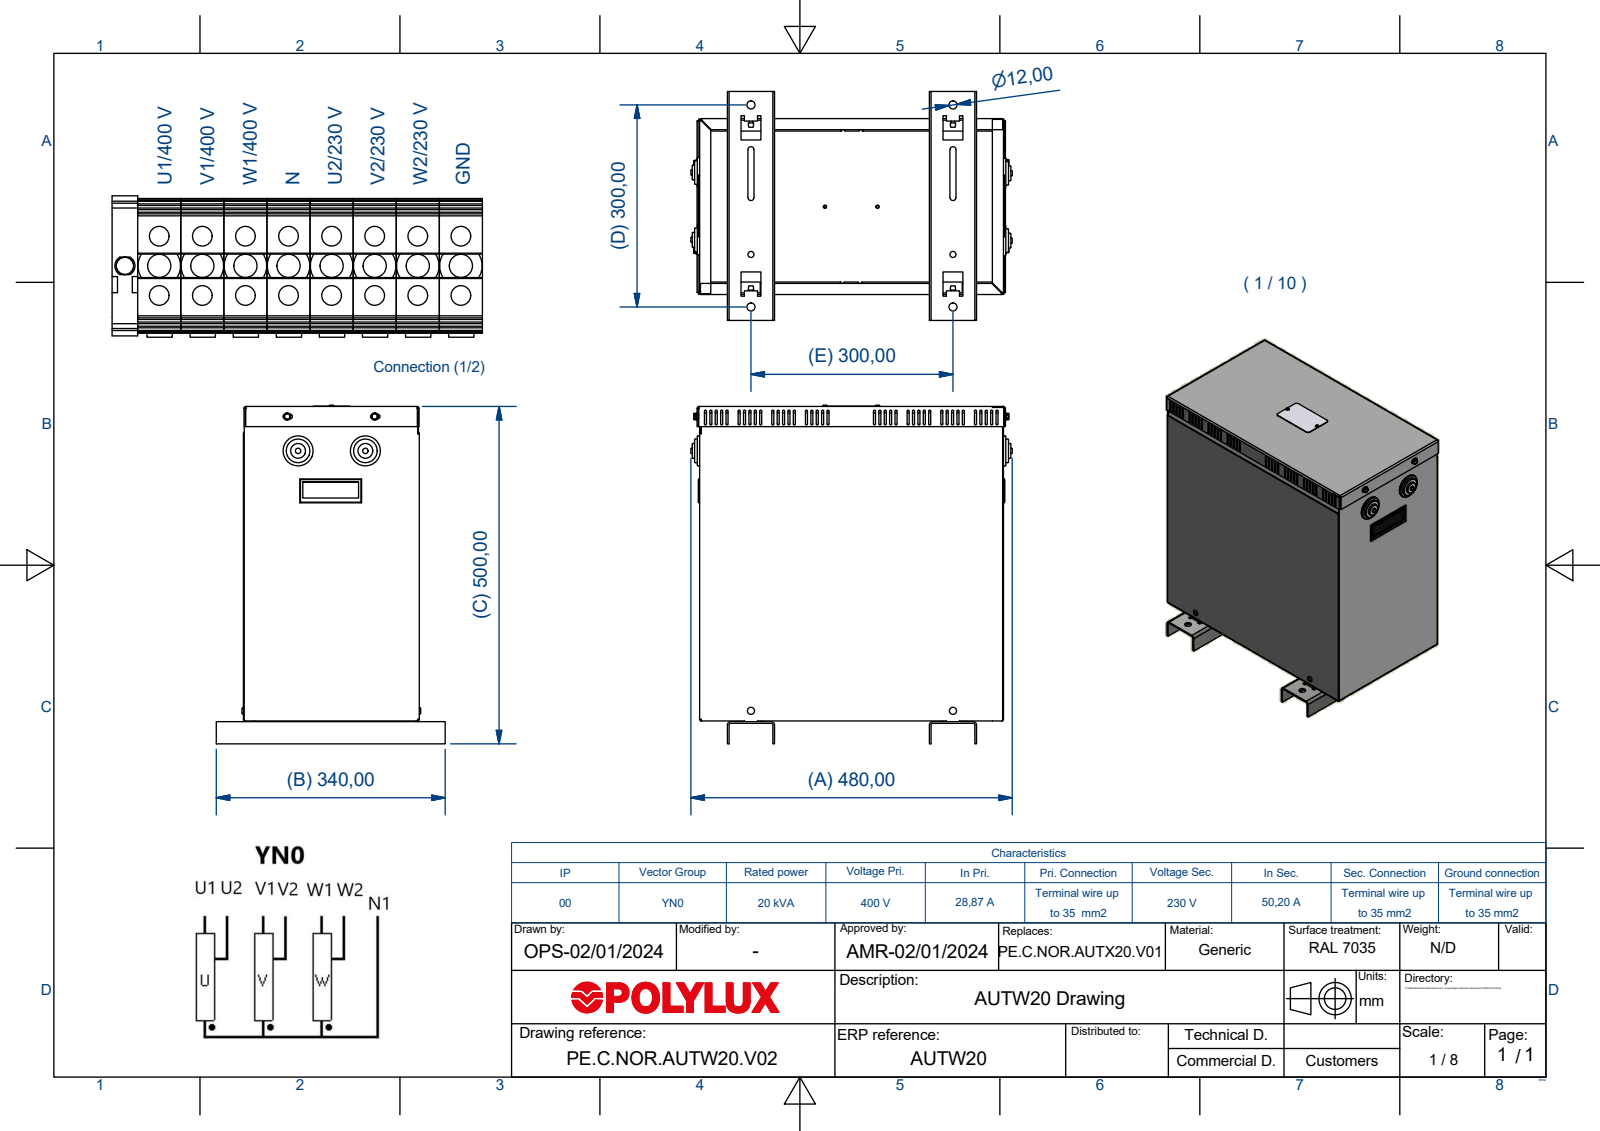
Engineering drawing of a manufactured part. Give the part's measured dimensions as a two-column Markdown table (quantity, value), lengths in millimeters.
| quantity | value |
| --- | --- |
| part name | AUTW20 |
| STEP written by | Autodesk Inventor 2018 (AUTOMOTIVE_DESIGN) |
| units | millimeters |
| bodies | 26 solids, 1132 faces (668 planar, 384 cylindrical, 80 other) |
| overall size | 502.8 × 477.2 × 340 |
| volume | 1 296 000 mm³ |
| surface area | 1 913 000 mm² |
| round holes (diameter × count) | 5.25 × 4, 5.6 × 4, 6 × 4, 8 × 4, 12 × 4, 20 × 4, 33 × 4, 36.5 × 4, 37 × 4, 42.5 × 4, 3.5 × 2, 4 × 2 |
| round bosses / shafts (diameter × count) | 5 × 6, 44.5 × 4, 38.5 × 4, 35 × 4, 22 × 4, 11 × 4, 8 × 4, 6.7 × 4 |
| partial cylindrical surfaces (radius × count) | 1.5 × 92, 3 × 14, 5 × 12, 1.2 × 10, 2.4 × 10, 0.2 × 8, 0.8 × 8, 2.5 × 8 |
| main face-to-face distances | 1.2, 260, 450, 258.8, 261.2, 1.5, 451.2, 448.8, 2.5, 67.5 |
| hole center spacings | 300, 1.2, 53.16, 125.8, 78, 52.83, 53.51, 100 |
